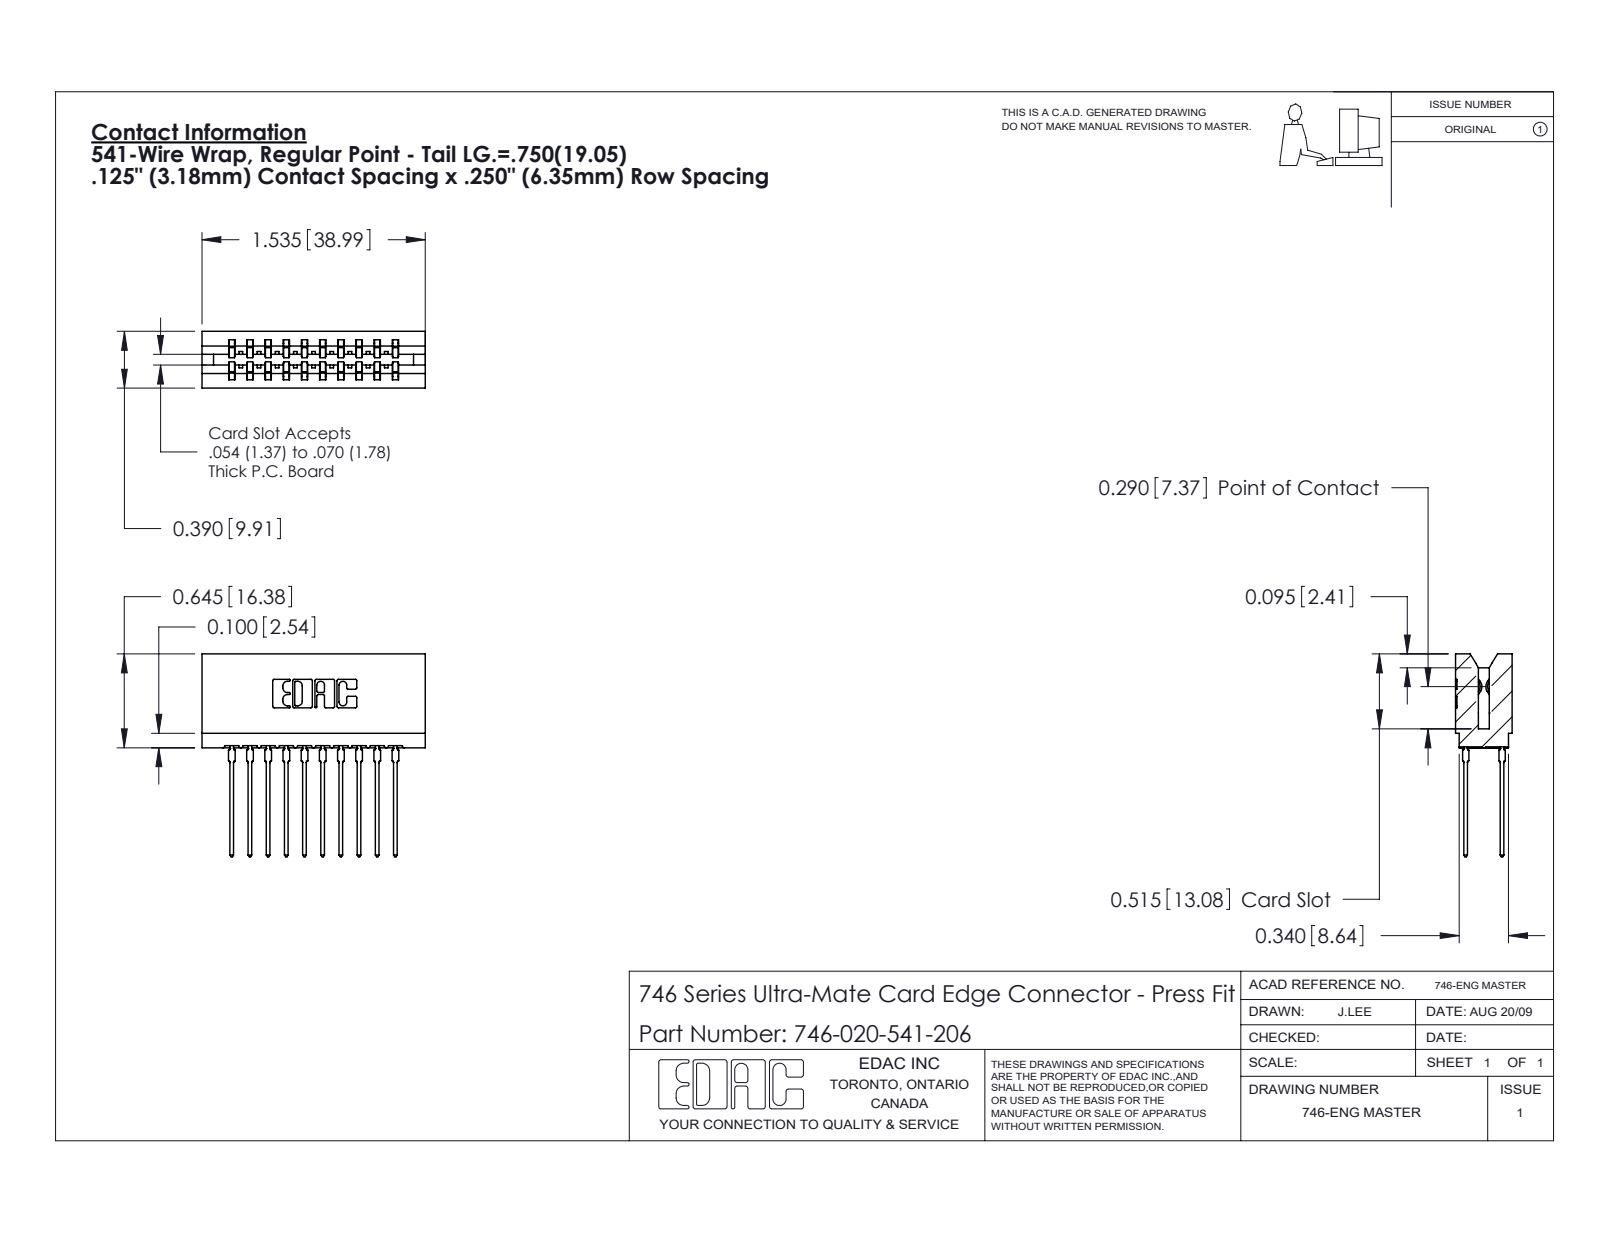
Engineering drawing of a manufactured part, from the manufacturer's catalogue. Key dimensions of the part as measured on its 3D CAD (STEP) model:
Part name (STEP PRODUCT): 746 Part_.515 Slot Depth - 06; 746-292-001_541; 746-020-541-206
STEP written by: SolidWorks 2020 (CONFIG_CONTROL_DESIGN)
Units: inches
Bodies: 21 solids, 1888 faces (976 planar, 392 cylindrical, 520 other)
Overall size (bounding box): 1.535 × 1.394 × 0.39
Volume: 0.273 in³ · Surface area: 10.96 in²
Partial cylindrical surfaces — rounded edges, fillets, slot ends (radius × count): R0.021 ×40, R0.01 ×22, R0.015 ×11, R0.005 ×8, R0.011 ×8, R0.007 ×6, R0.031 ×6, R0.026 ×3
Main face-to-face distances: 0.25, 0.333, 0.057, 0.5, 0.042, 0.125, 0.083, 0.025, 0.292, 0.75
